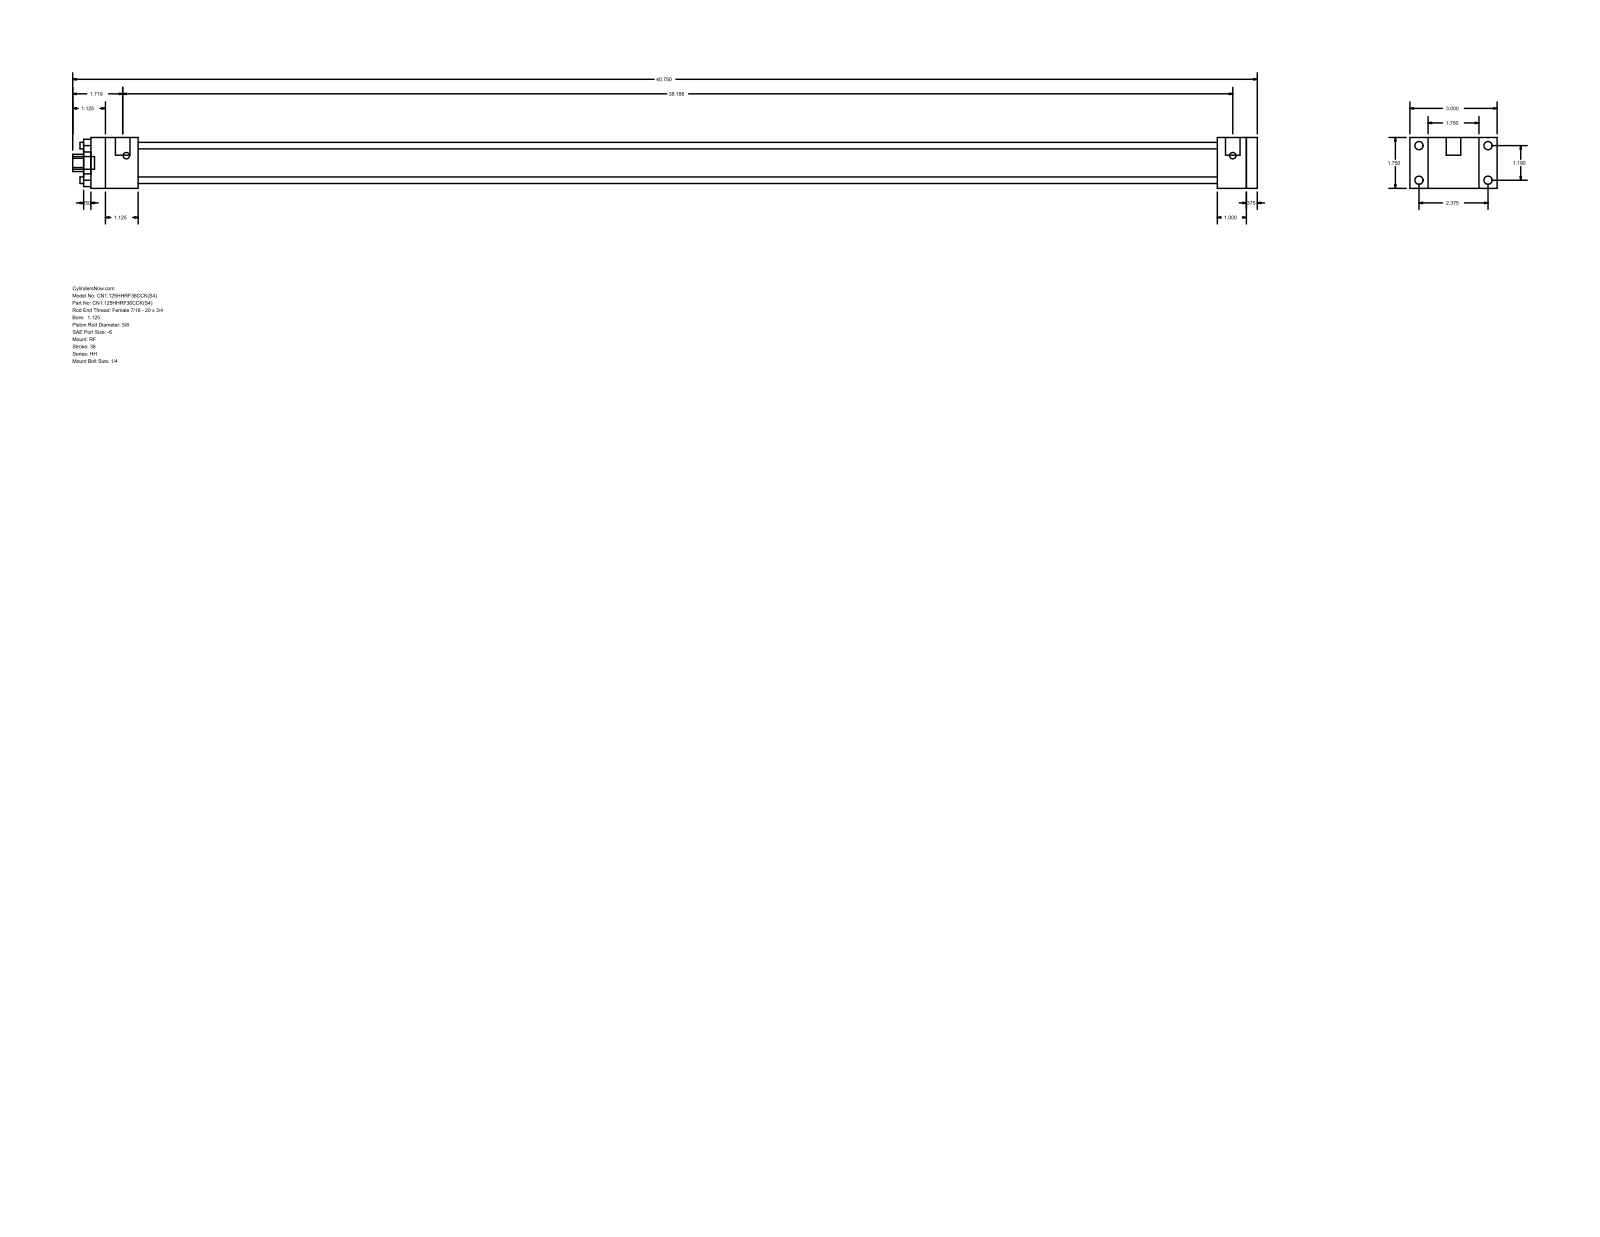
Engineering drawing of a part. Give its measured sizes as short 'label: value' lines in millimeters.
name: HH_RF__0112_0.625
written by: GSSL Pune (CONFIG_CONTROL_DESIGN)
unit: mm
bodies: 0 solids, 92 faces (64 planar, 28 cylindrical, 0 other)
size: 1035.05 × 76.2 × 44.45
holes: 4× ⌀5.71, 1× ⌀15.88, 1× ⌀28.57, 1× ⌀34.92
bosses: 4× ⌀7.14, 4× ⌀5.56, 2× ⌀12.7, 1× ⌀11.11
rounds: 1× R7.54
face distances: 44.46, 9.52, 15.87, 968.38, 977.9, 942.97, 25.41, 34.93, 41.27, 984.24
hole spacings: 21.37, 30.22, 42.74
